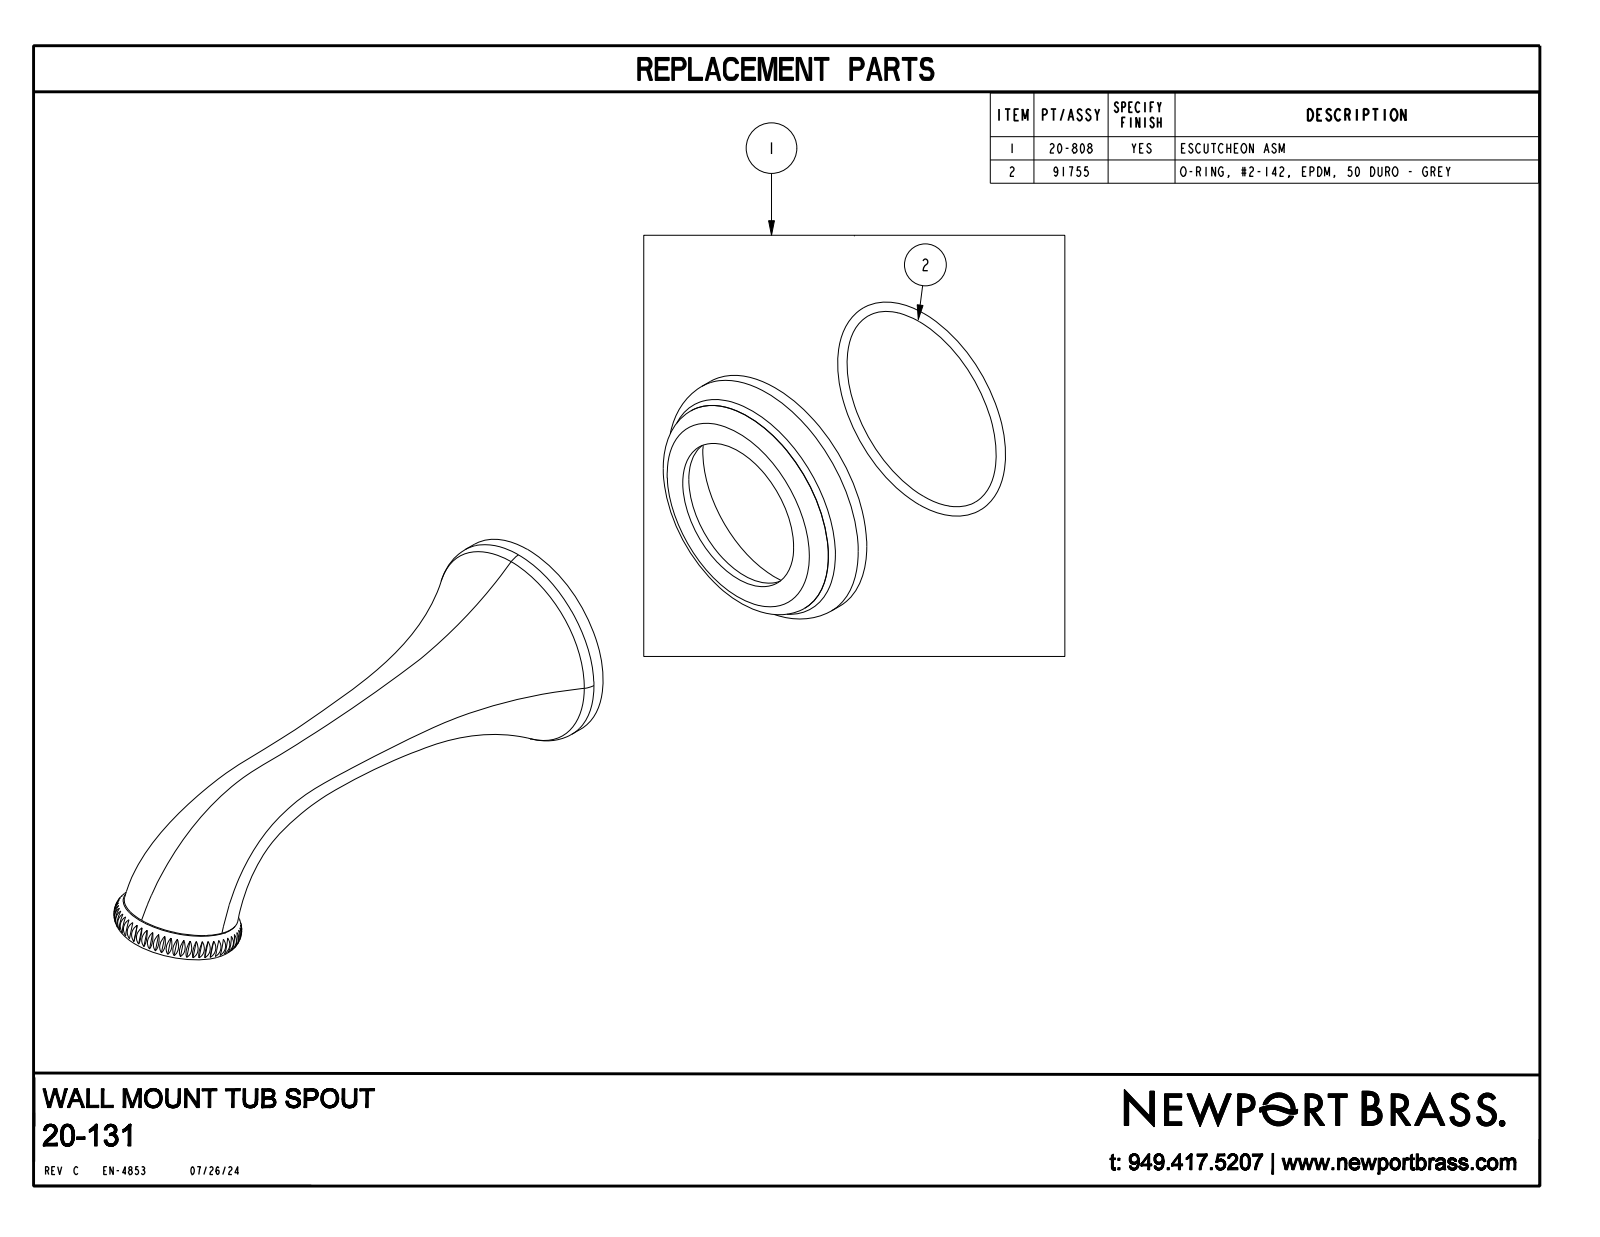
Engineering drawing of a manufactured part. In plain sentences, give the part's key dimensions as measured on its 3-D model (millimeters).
The part is named "20-131_SW". Its 3-D file was written by "CREO PARAMETRIC BY PTC INC, 2018400 (AUTOMOTIVE_DESIGN)". It is 1 solid with 149 faces: 125 planar, 8 cylindrical and 16 other. Overall it measures 170.5 by 72.4 by 72.4 millimeters. Its volume is 173 200 cubic millimeters and its surface area 24 570 square millimeters. Round bosses or shafts: 1 of diameter 72.4, 1 of diameter 63.7, 1 of diameter 59.6, 1 of diameter 29.3. The main face-to-face distances are 14.6, 7.4, 24.5, 7.5, 24.5, 24.5, 24.5, 24.5.
